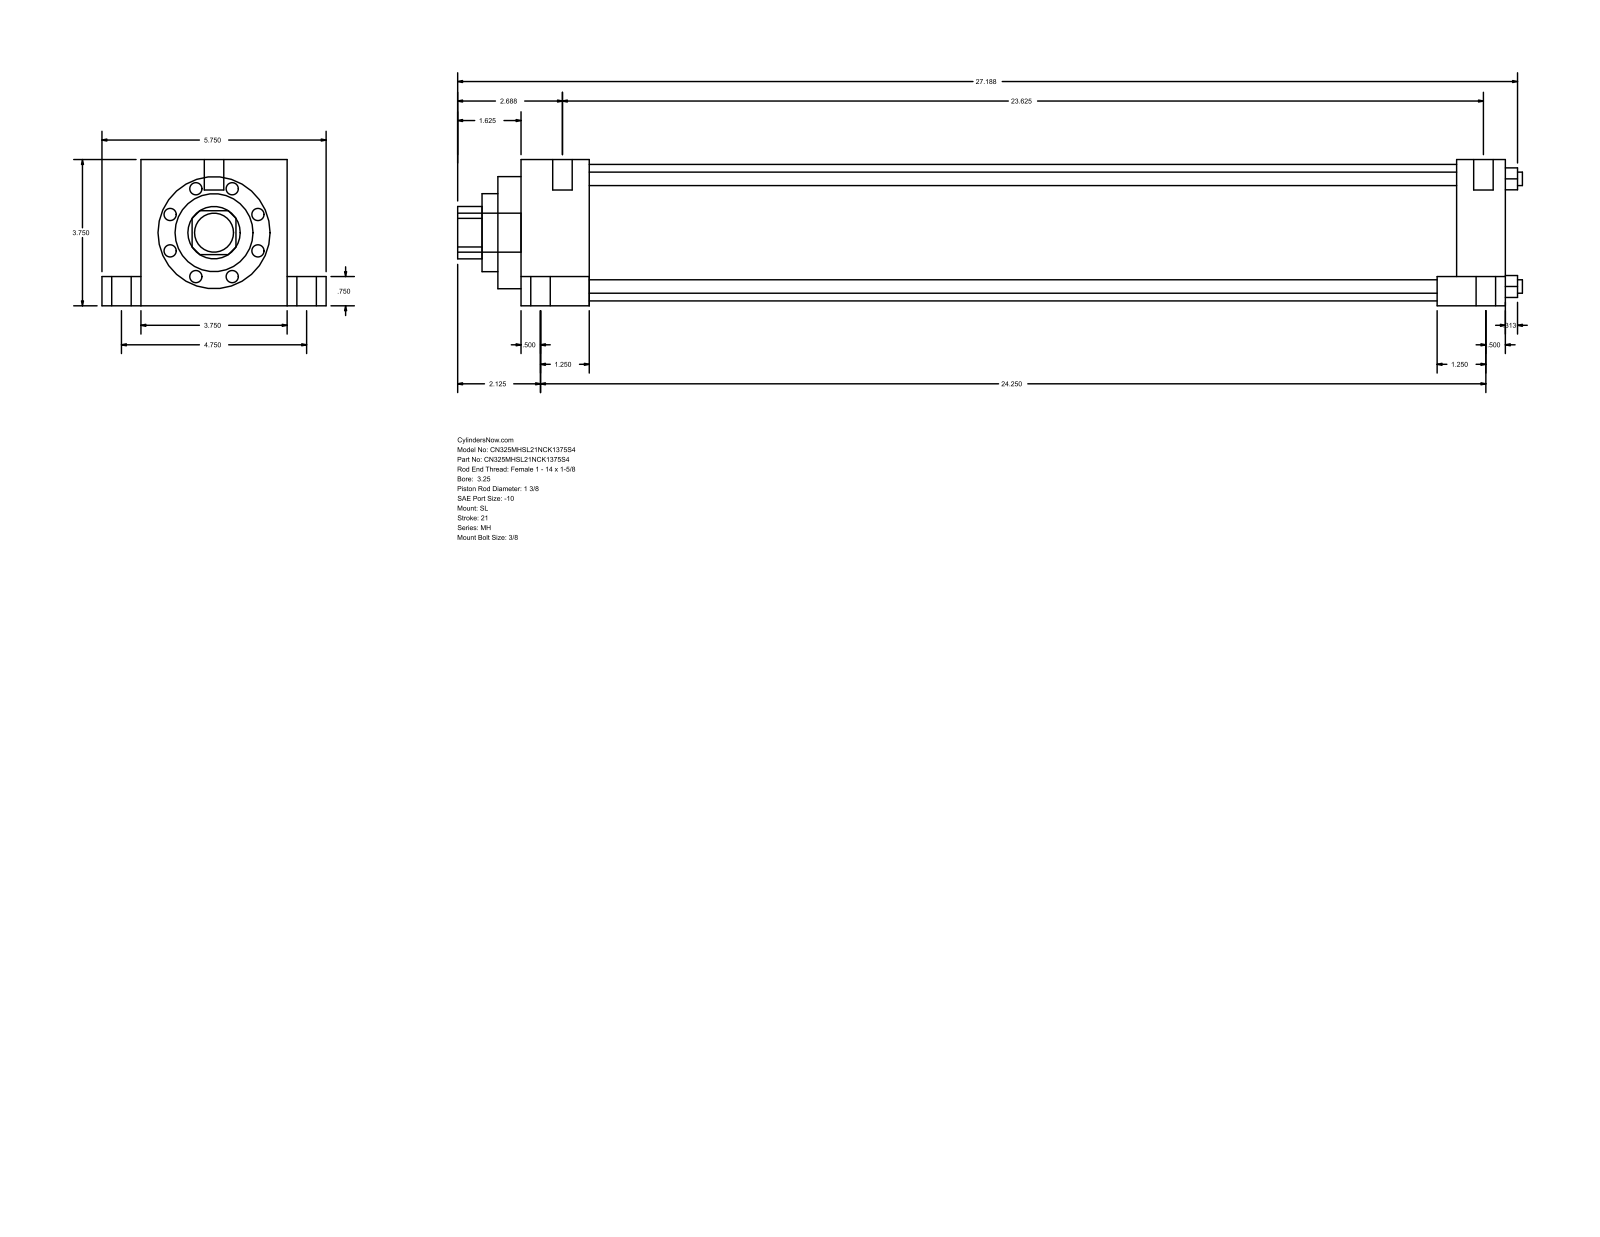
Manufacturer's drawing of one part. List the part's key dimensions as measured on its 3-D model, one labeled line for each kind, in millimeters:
Part name (STEP PRODUCT): MH_SL__0325_1.375
STEP written by: GSSL Pune (CONFIG_CONTROL_DESIGN)
Units: millimetres
Bodies: 0 solids, 110 faces (77 planar, 33 cylindrical, 0 other)
Overall size (bounding box): 693.74 × 146.05 × 95.25
Round holes (diameter × count): ⌀8.76 ×4, ⌀34.92 ×1, ⌀50.8 ×1, ⌀73.03 ×1, ⌀88.9 ×1
Round bosses / shafts (diameter × count): ⌀12.7 ×6, ⌀19.05 ×4, ⌀5.56 ×4, ⌀25.4 ×1
Partial cylindrical surfaces — rounded edges, fillets, slot ends (radius × count): R17.06 ×1
Main face-to-face distances: 95.24, 641.35, 44.45, 596.9, 25.41, 120.65, 19.05, 76.19, 609.61, 565.16
Hole centre spacings: 49.57, 70.1, 99.14
